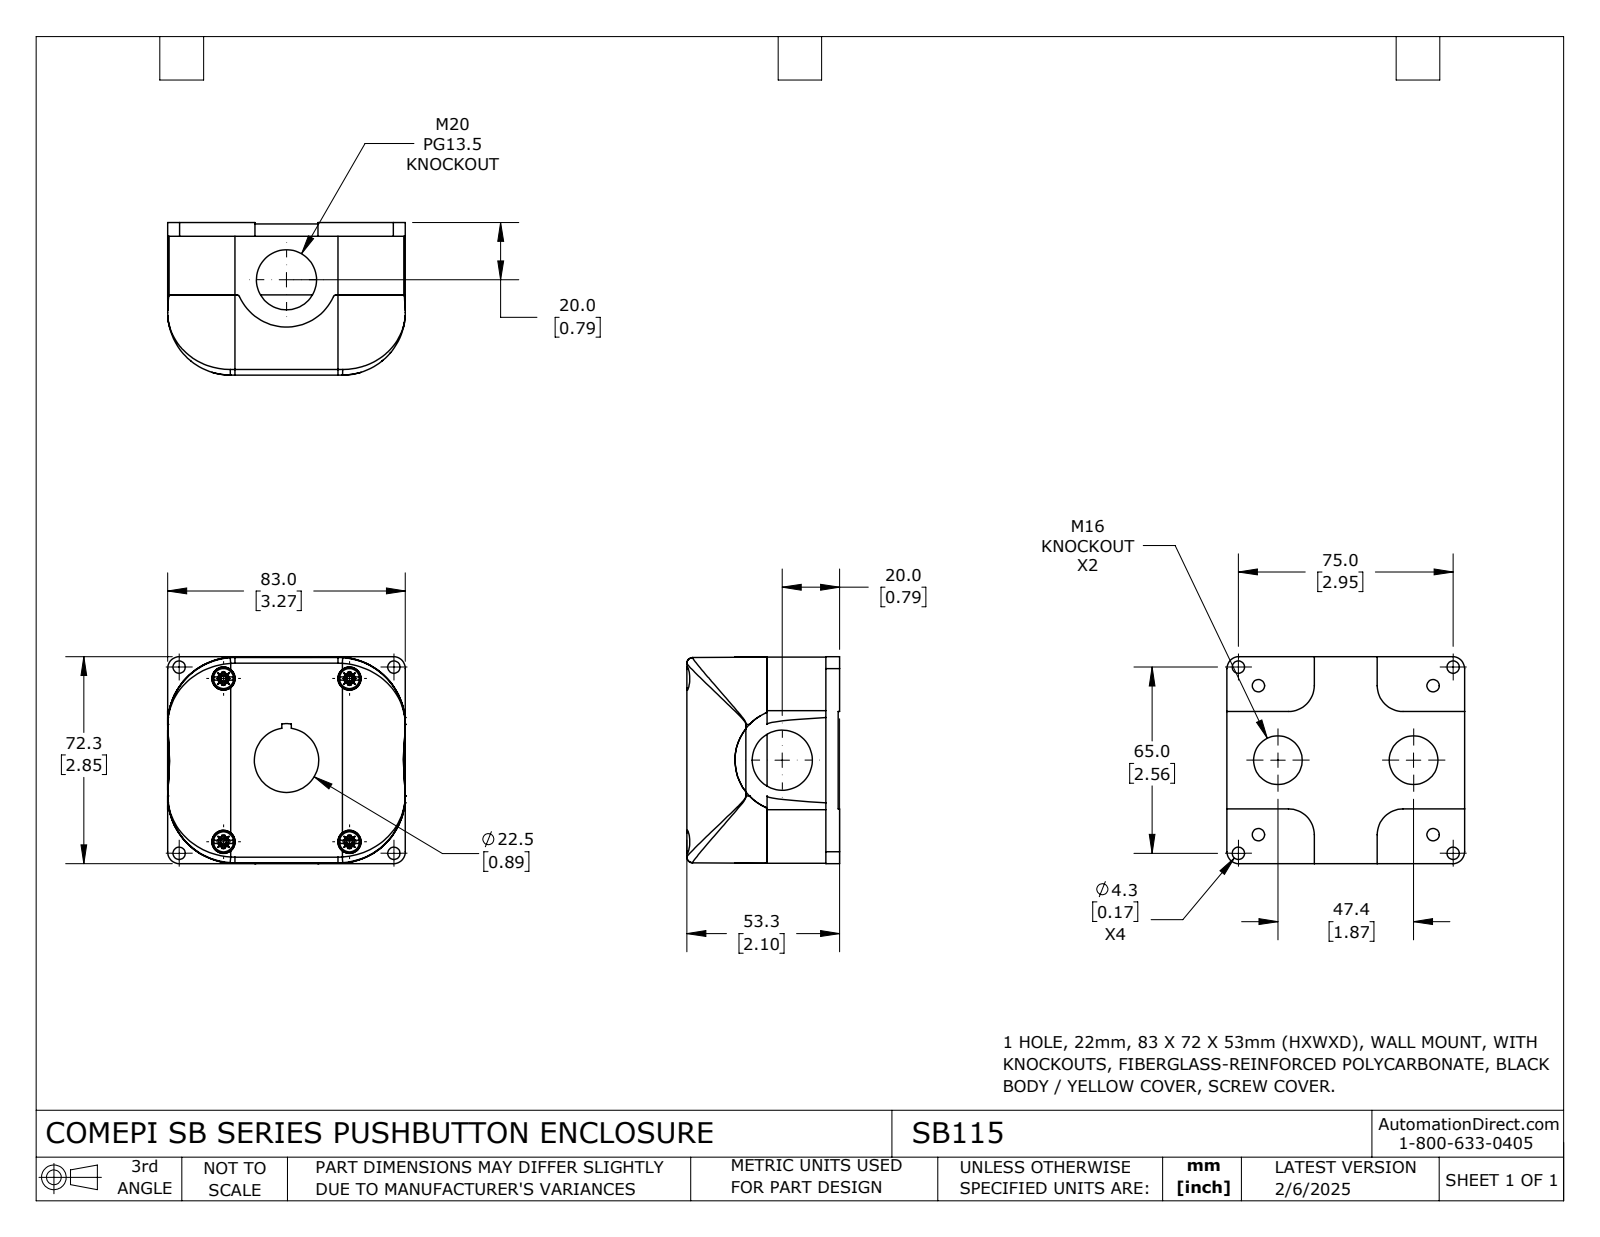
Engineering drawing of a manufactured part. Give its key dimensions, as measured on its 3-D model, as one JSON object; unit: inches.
{"part_name": "SB115", "step_written_by": "SolidWorks 2024 (CONFIG_CONTROL_DESIGN)", "units": "inches", "bodies": {"solids": 2, "faces": 463, "planar": 273, "cylindrical": 114, "other": 76}, "overall_size": [3.268, 2.846, 2.098], "volume_in3": 12.51, "surface_area_in2": 79.33, "round_holes": [[0.169, 8], [0.323, 4], [0.669, 2], [0.827, 2]], "round_bosses_or_shafts": [[0.276, 4]], "partial_cylinders_radius": [[0.035, 4], [0.079, 4], [0.354, 4], [0.38, 4], [0.925, 4], [0.709, 2], [0.835, 2], [0.866, 2]], "face_to_face_distances": [0.976, 0.878, 0.098, 2.079, 1.98, 1.102, 0.118, 0.02, 0.996, 2.098], "hole_center_spacings": [0.376, 1.058, 1.39, 2.32, 2.367, 2.689, 2.728, 3.531]}
